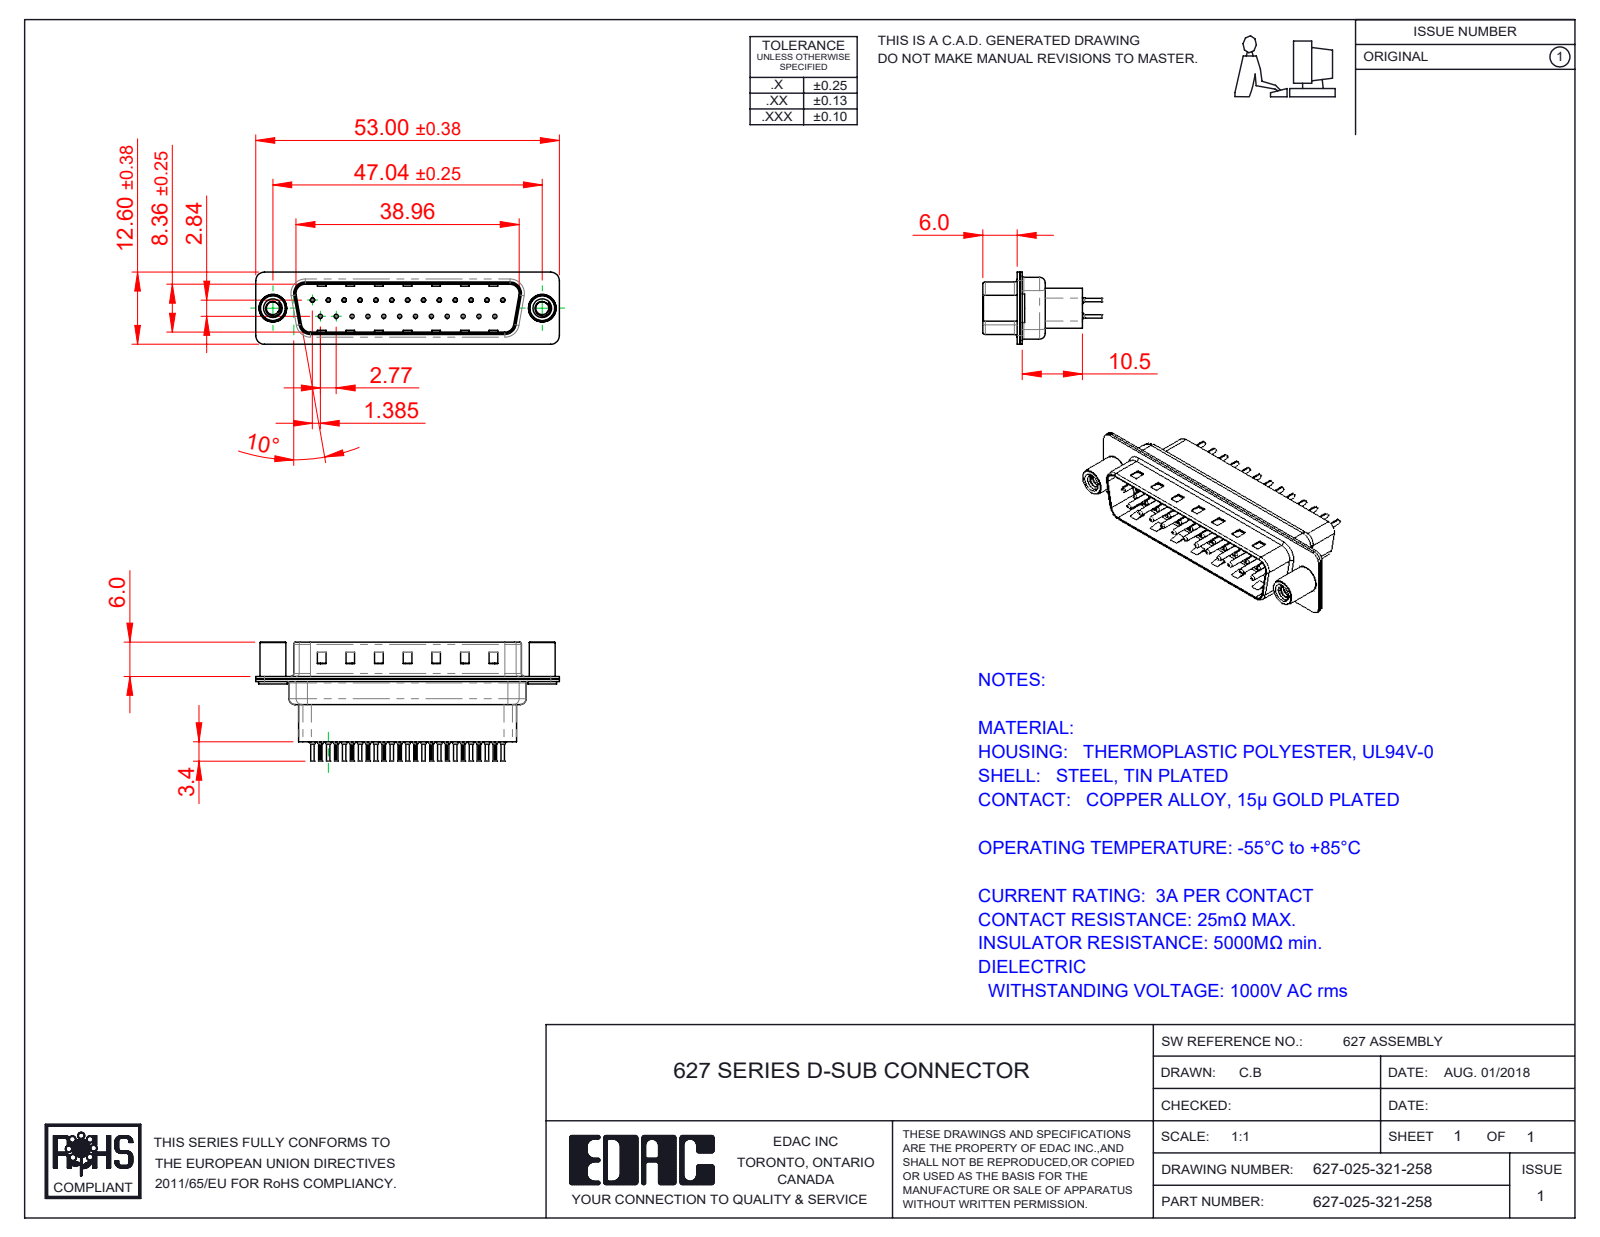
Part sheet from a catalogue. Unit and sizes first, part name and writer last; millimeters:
Units: millimetres
Overall size (bounding box): 53 × 20.8 × 12.6
Round holes (diameter × count): ⌀0.2 ×25, ⌀0.35 ×25, ⌀1.1 ×25, ⌀1.6 ×25, ⌀2.26 ×2, ⌀4 ×2, ⌀4.8 ×2
Round bosses / shafts (diameter × count): ⌀2 ×25, ⌀1.5 ×25, ⌀0.75 ×25, ⌀0.6 ×25, ⌀5 ×2, ⌀4.9 ×2, ⌀4.5 ×2
Partial cylindrical surfaces — rounded edges, fillets, slot ends (radius × count): R0.1 ×50, R1.5 ×16, R2 ×12, R0.5 ×8, R1.6 ×8, R0.25 ×4, R0.6 ×4, R0.65 ×4
Main face-to-face distances: 0.4, 0.45, 0.82, 9.58, 0.68, 7.68, 0.9, 1.5, 1.08, 8.08
Hole centre spacings: 3.16, 8.31, 2.77, 5.54, 11.08, 16.62, 5.03, 5.04
Volume: 3 862 mm³ · Surface area: 9 972 mm²
Bodies: 30 solids, 2860 faces (773 planar, 1090 cylindrical, 997 other)
Part name (STEP PRODUCT): 627-025-321-058; 627 Contact Row 2_21H; 627 Shell Front_25 Contacts; 627 4-40 Threaded Standoff (+3 more)
STEP written by: SolidWorks 2020 (CONFIG_CONTROL_DESIGN)
